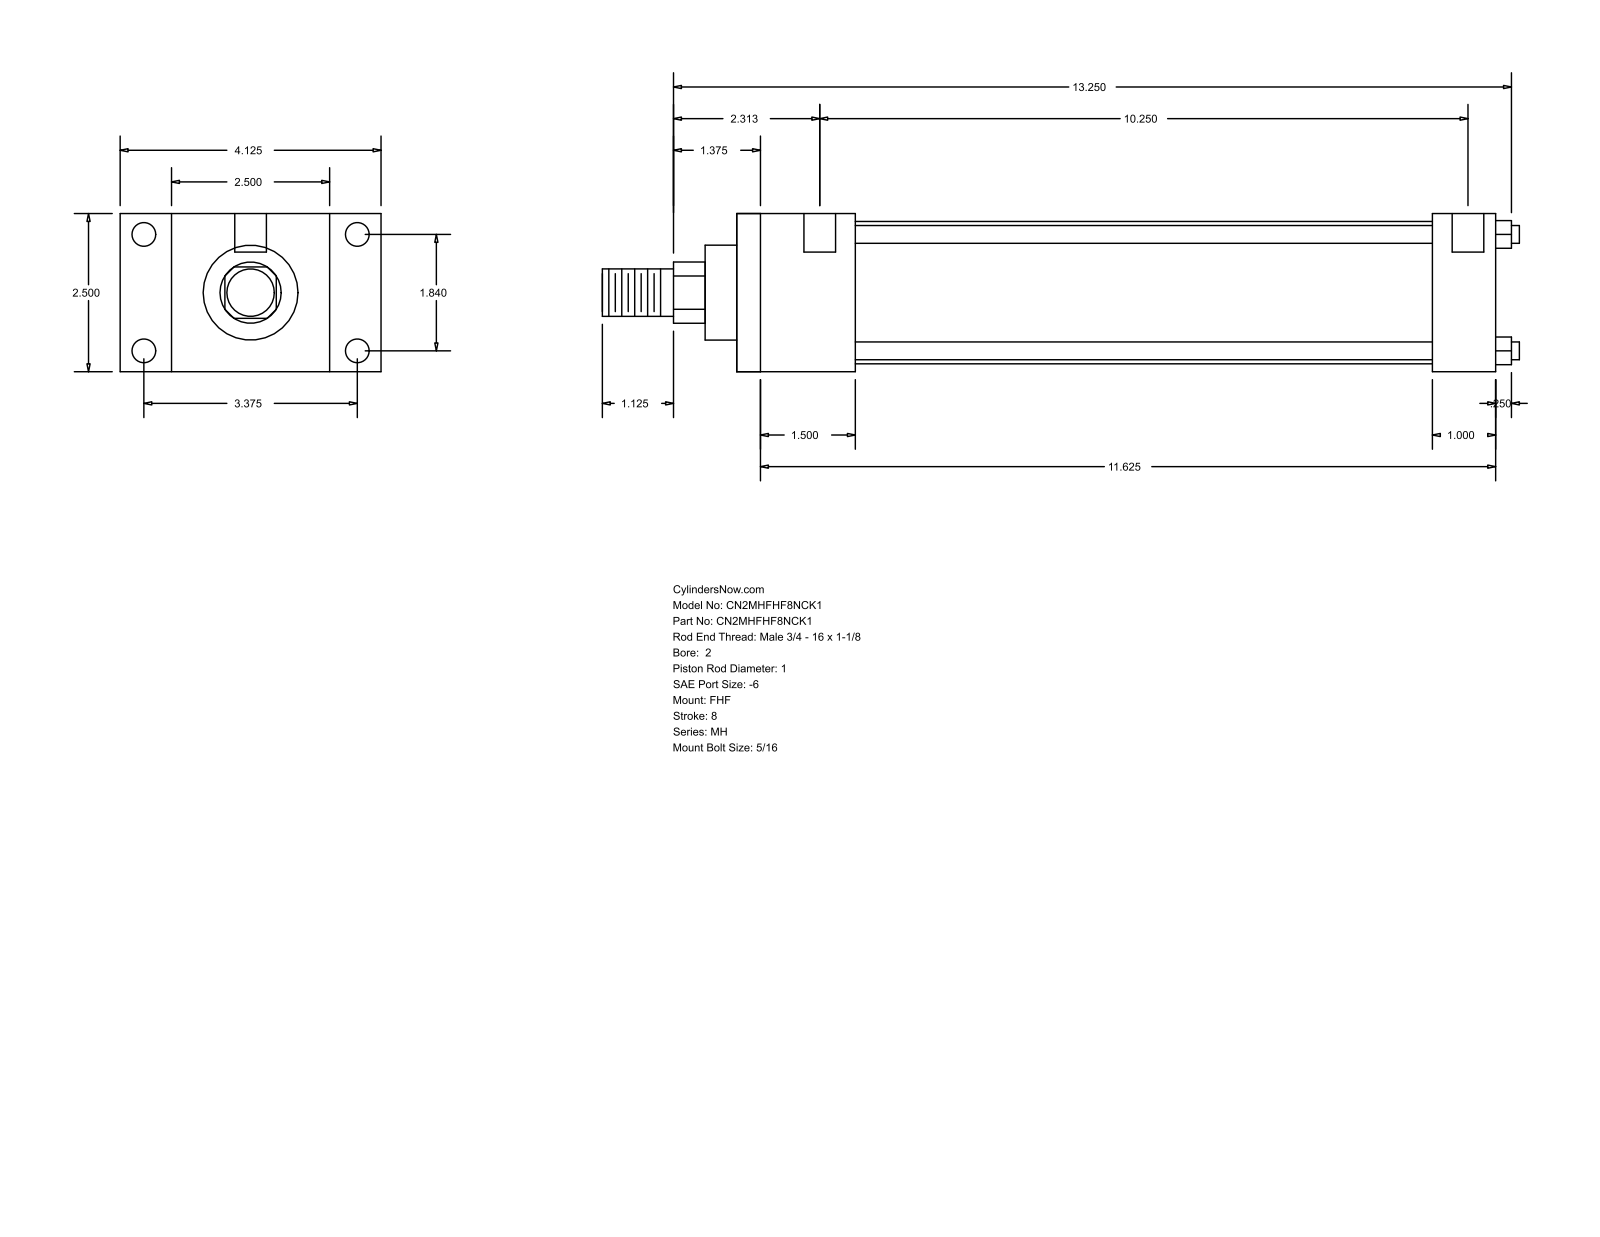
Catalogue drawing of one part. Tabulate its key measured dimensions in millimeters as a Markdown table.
| quantity | value |
| --- | --- |
| part name | MH_FHF__0200_1 |
| STEP written by | GSSL Pune (CONFIG_CONTROL_DESIGN) |
| units | millimeters |
| bodies | 0 solids, 88 faces (60 planar, 28 cylindrical, 0 other) |
| overall size | 368.3 × 104.78 × 63.5 |
| round holes (diameter × count) | 5.56 × 4, 9.53 × 4, 12.7 × 2 |
| round bosses / shafts (diameter × count) | 7.14 × 4, 57.15 × 1, 38.1 × 1, 25.4 × 1, 19.05 × 1 |
| partial cylindrical surfaces (radius × count) | 12.29 × 1 |
| main face-to-face distances | 63.5, 304.8, 47.63, 257.17, 20.64, 84.14, 104.78, 25.4, 279.4, 231.77 |
| hole center spacings | 46.74, 85.72, 97.63, 268.28, 3.17, 4.76, 260.35, 263.52 |
